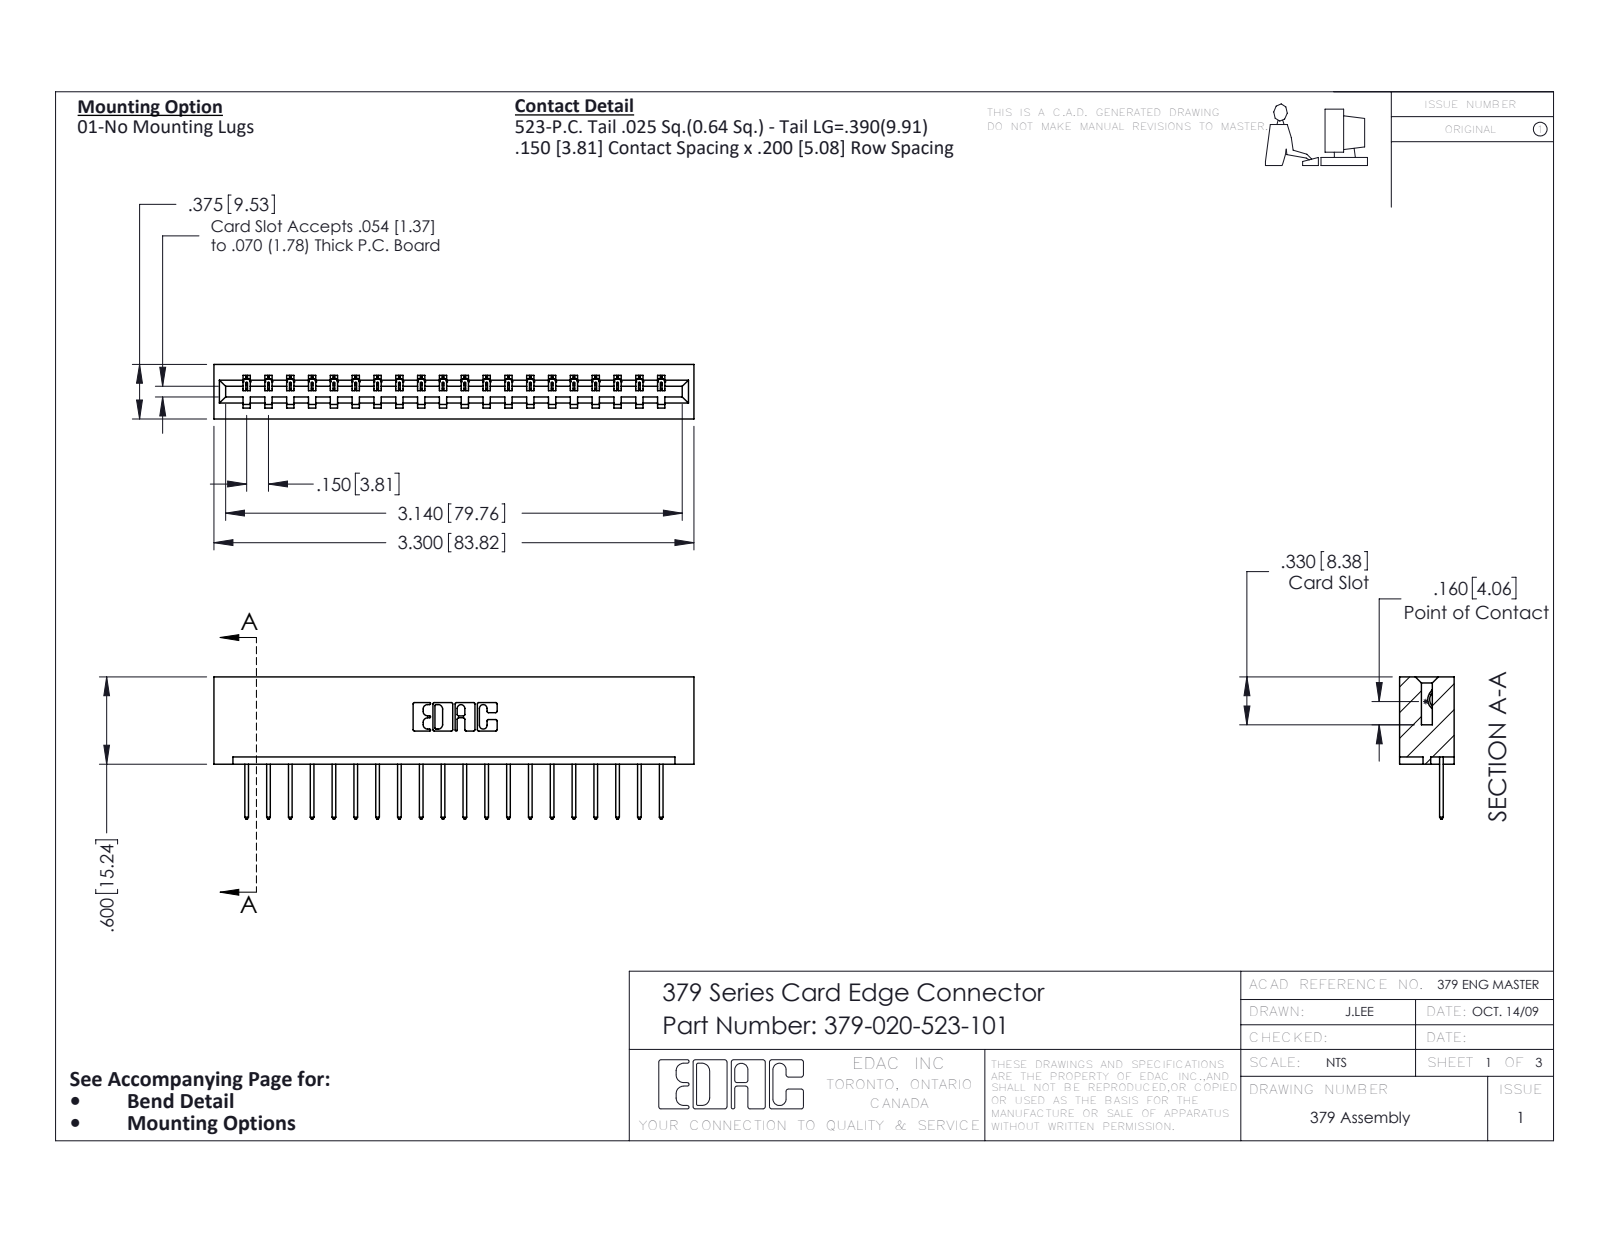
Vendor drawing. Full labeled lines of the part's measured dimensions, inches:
Part name (STEP PRODUCT): 345-292-001_345-293-123; 379-020-523-101; 379 Part_Lugless
STEP written by: SolidWorks 2016 (CONFIG_CONTROL_DESIGN)
Units: inches
Bodies: 21 solids, 1266 faces (906 planar, 360 cylindrical, 0 other)
Overall size (bounding box): 3.3 × 0.977 × 0.375
Volume: 0.565 in³ · Surface area: 14.48 in²
Partial cylindrical surfaces — rounded edges, fillets, slot ends (radius × count): R0.006 ×40, R0.01 ×40, R0.01 ×22, R0.007 ×6, R0.031 ×6, R0.026 ×3, R0.014 ×1, R0.022 ×1
Main face-to-face distances: 0.3, 0.075, 0.375, 0.6, 0.225, 0.15, 0.45, 0.75, 0.9, 0.1
